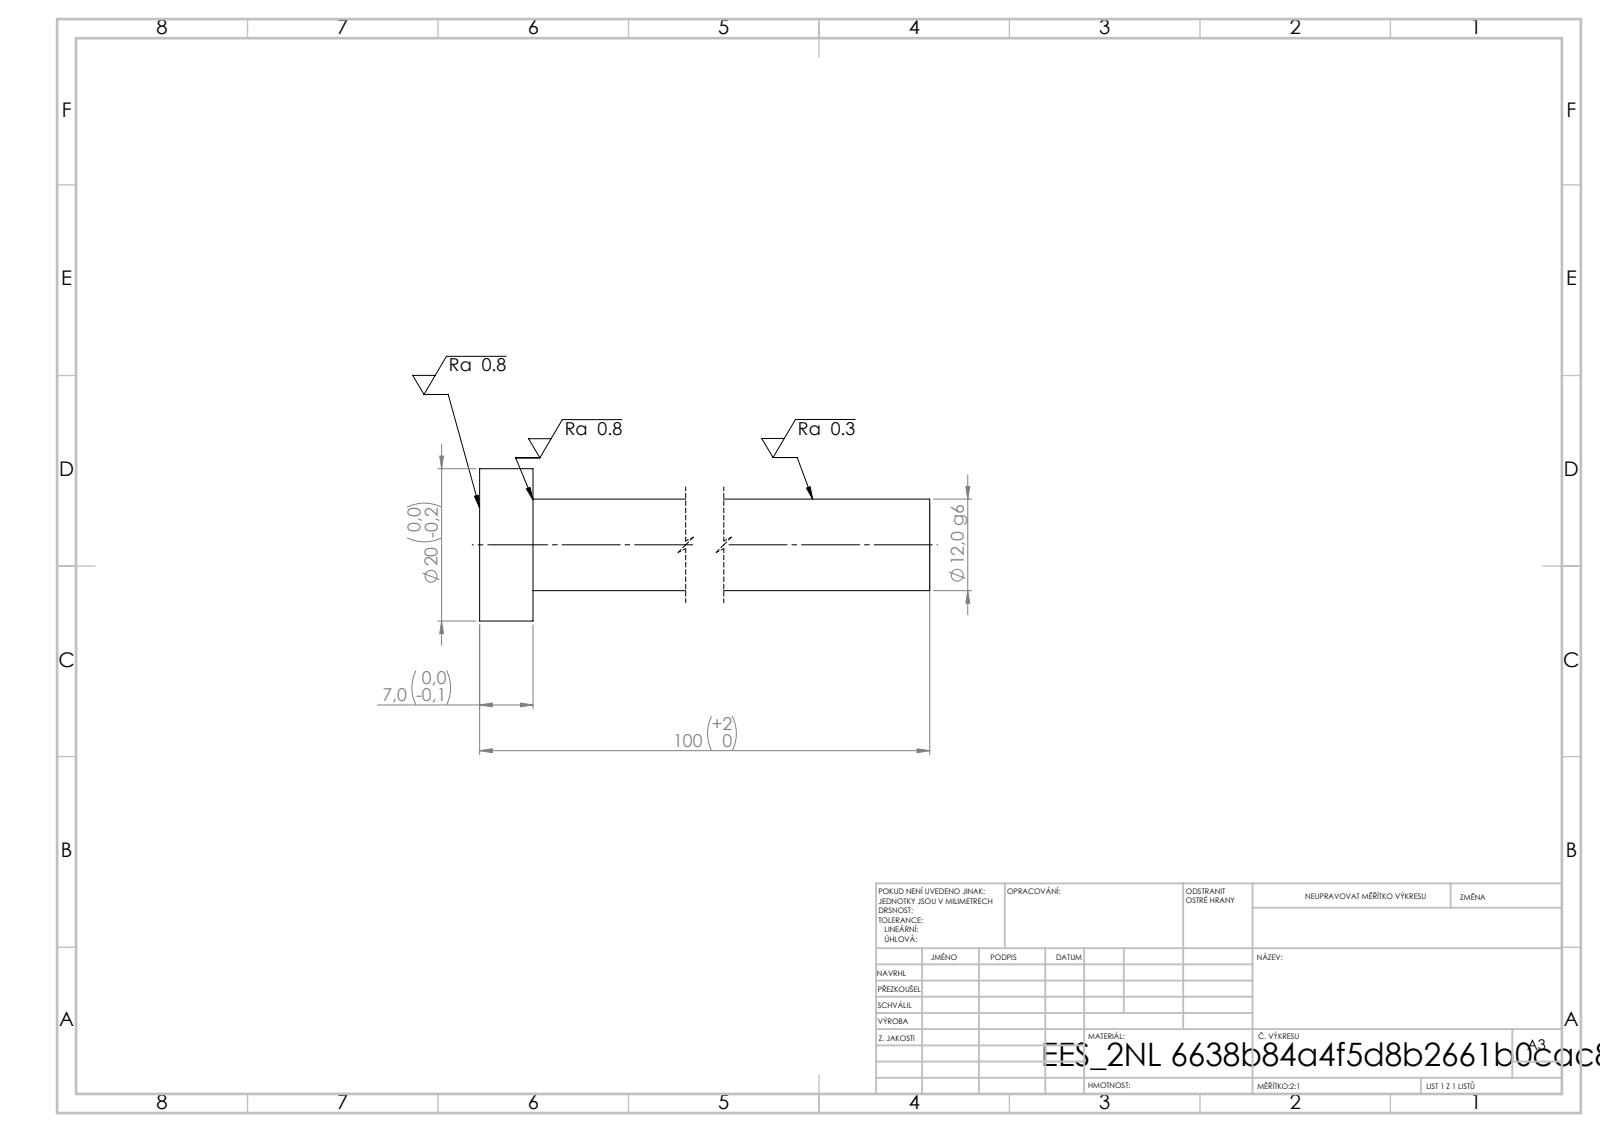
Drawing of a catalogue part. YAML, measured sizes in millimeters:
step_written_by: "SolidWorks 2019 (CONFIG_CONTROL_DESIGN)"
units: millimeters
bodies: {solids: 1, faces: 7, planar: 3, cylindrical: 4, other: 0}
overall_size: [100, 20, 20]
volume: 12717
surface_area: 4574
round_bosses_or_shafts:
  - {diameter: 20, count: 1}
  - {diameter: 12, count: 1}
face_to_face_distances: [7, 100, 93]
